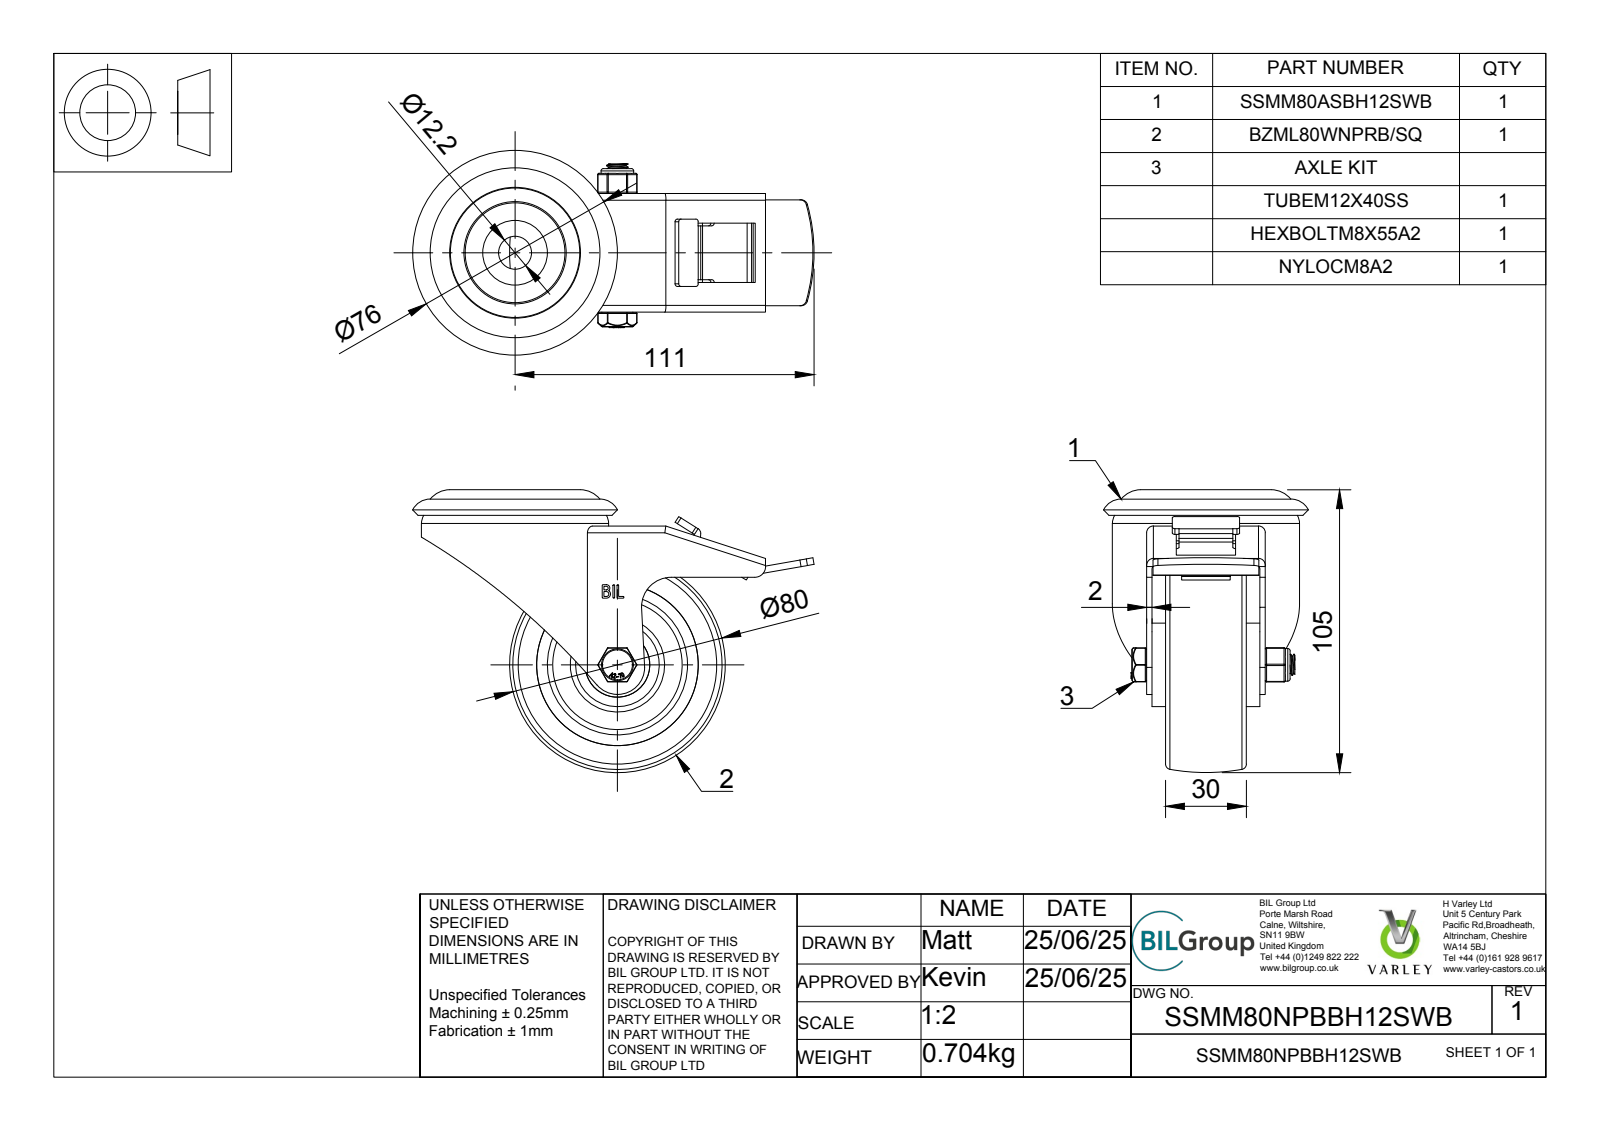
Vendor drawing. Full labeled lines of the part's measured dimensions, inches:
Part name (STEP PRODUCT): SSMM80NPBBH12SWB v3; SSMM80ASBH12SWB v1; STAINLESS STEEL HEAD; STAINLESS STEEL FORKS (+8 more)
STEP written by: Autodesk Translation Framework v14.10.0.0 (AUTOMOTIVE_DESIGN)
Units: inches
Bodies: 18 solids, 678 faces (330 planar, 220 cylindrical, 128 other)
Overall size (bounding box): 5.867 × 4.134 × 2.992
Volume: 11.11 in³ · Surface area: 165.1 in²
Round holes (diameter × count): ⌀0.315 ×1, ⌀0.323 ×1, ⌀0.335 ×1, ⌀0.339 ×1, ⌀0.48 ×1, ⌀0.492 ×1, ⌀0.906 ×1, ⌀0.945 ×1, ⌀2.047 ×1, ⌀2.362 ×1, ⌀2.559 ×1, ⌀2.835 ×1
Round bosses / shafts (diameter × count): ⌀0.217 ×6, ⌀2.736 ×1, ⌀1.949 ×1, ⌀1.496 ×1, ⌀1.22 ×1, ⌀0.945 ×1, ⌀0.886 ×1, ⌀0.839 ×1
Partial cylindrical surfaces — rounded edges, fillets, slot ends (radius × count): R0.03 ×48, R0.02 ×26, R0.01 ×12, R0.098 ×7, R0.039 ×6, R0.049 ×6, R0.079 ×5, R0.059 ×1
Main face-to-face distances: 0.079, 0.197, 1.378, 0.276, 0.098, 1.457, 1.654, 1.575, 1.181, 0.177
